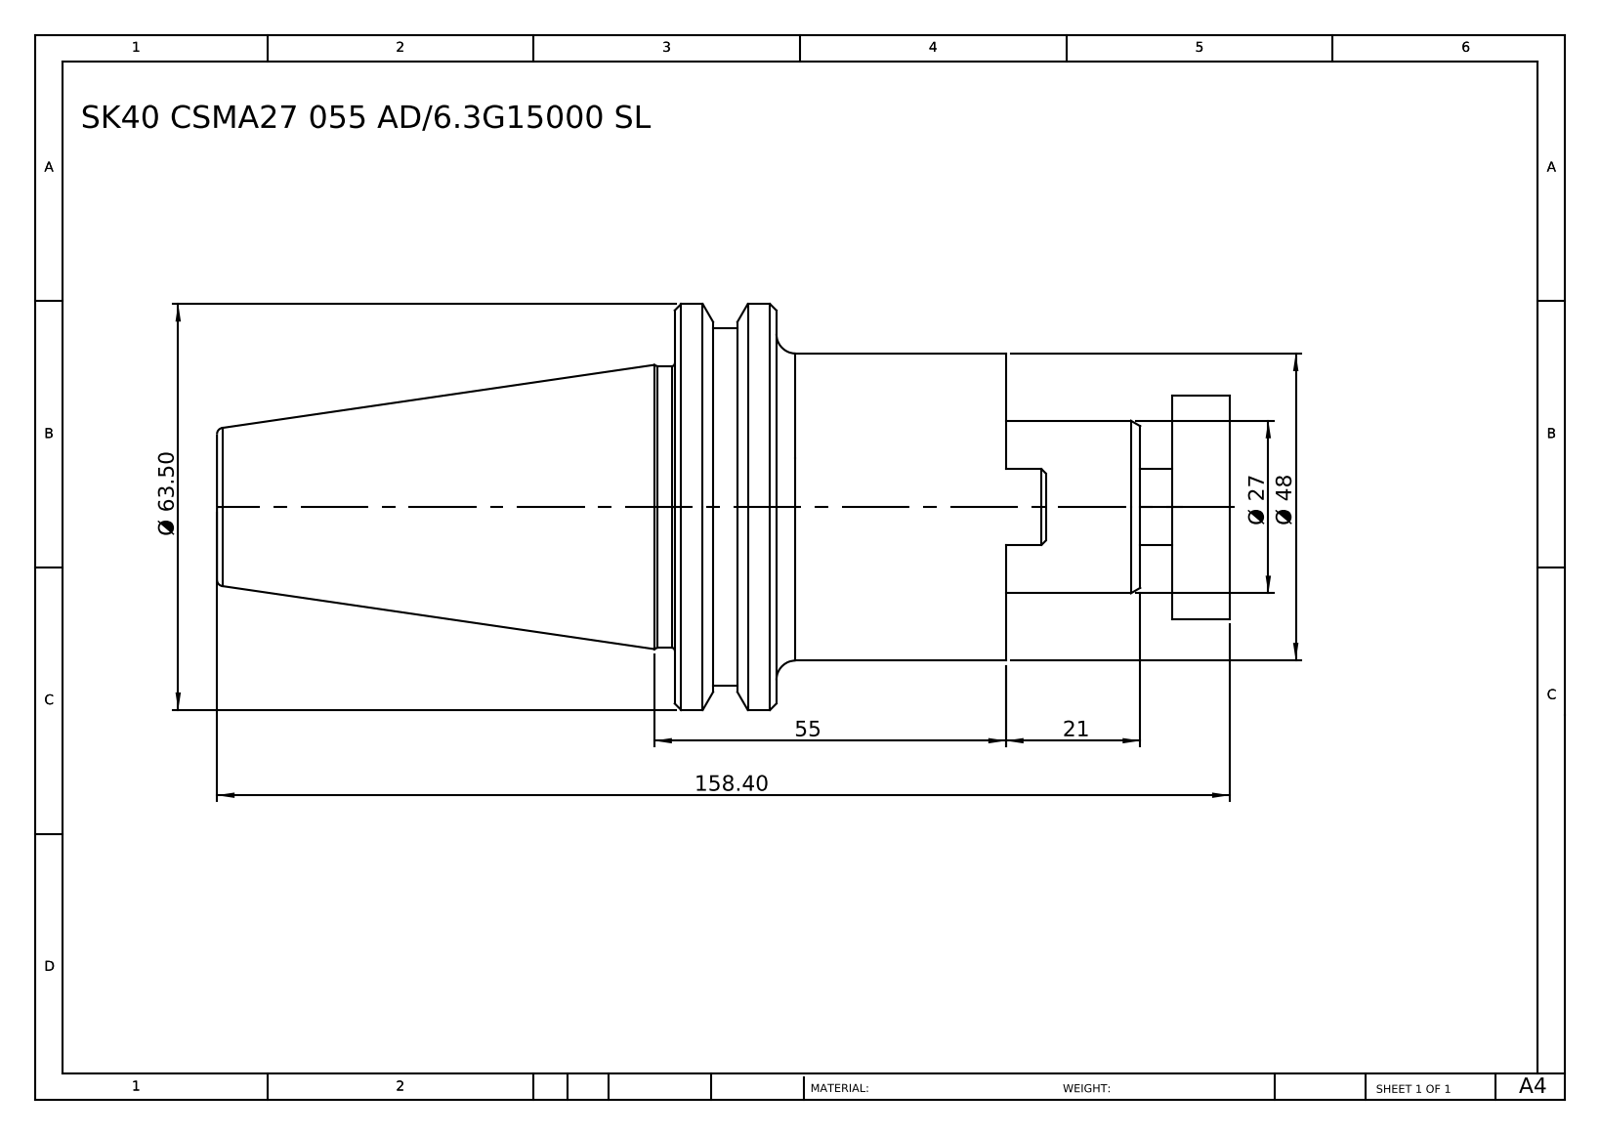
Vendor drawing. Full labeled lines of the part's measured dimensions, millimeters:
Part name (STEP PRODUCT): SK 40 CSMA27 055 AD-6.3G15000 SL SP
STEP written by: SolidWorks 2014 (CONFIG_CONTROL_DESIGN)
Units: millimetres
Bodies: 1 solid, 59 faces (20 planar, 16 cylindrical, 23 other)
Overall size (bounding box): 158.4 × 63.5 × 63.5
Volume: 205 164 mm³ · Surface area: 27 007 mm²
Round bosses / shafts (diameter × count): ⌀63.5 ×1, ⌀56 ×1, ⌀48 ×1, ⌀44 ×1, ⌀35 ×1, ⌀27 ×1, ⌀12 ×1
Main face-to-face distances: 51.8, 35, 86.8, 9, 26, 77.8, 70.9, 61.9, 35.9, 15.9
